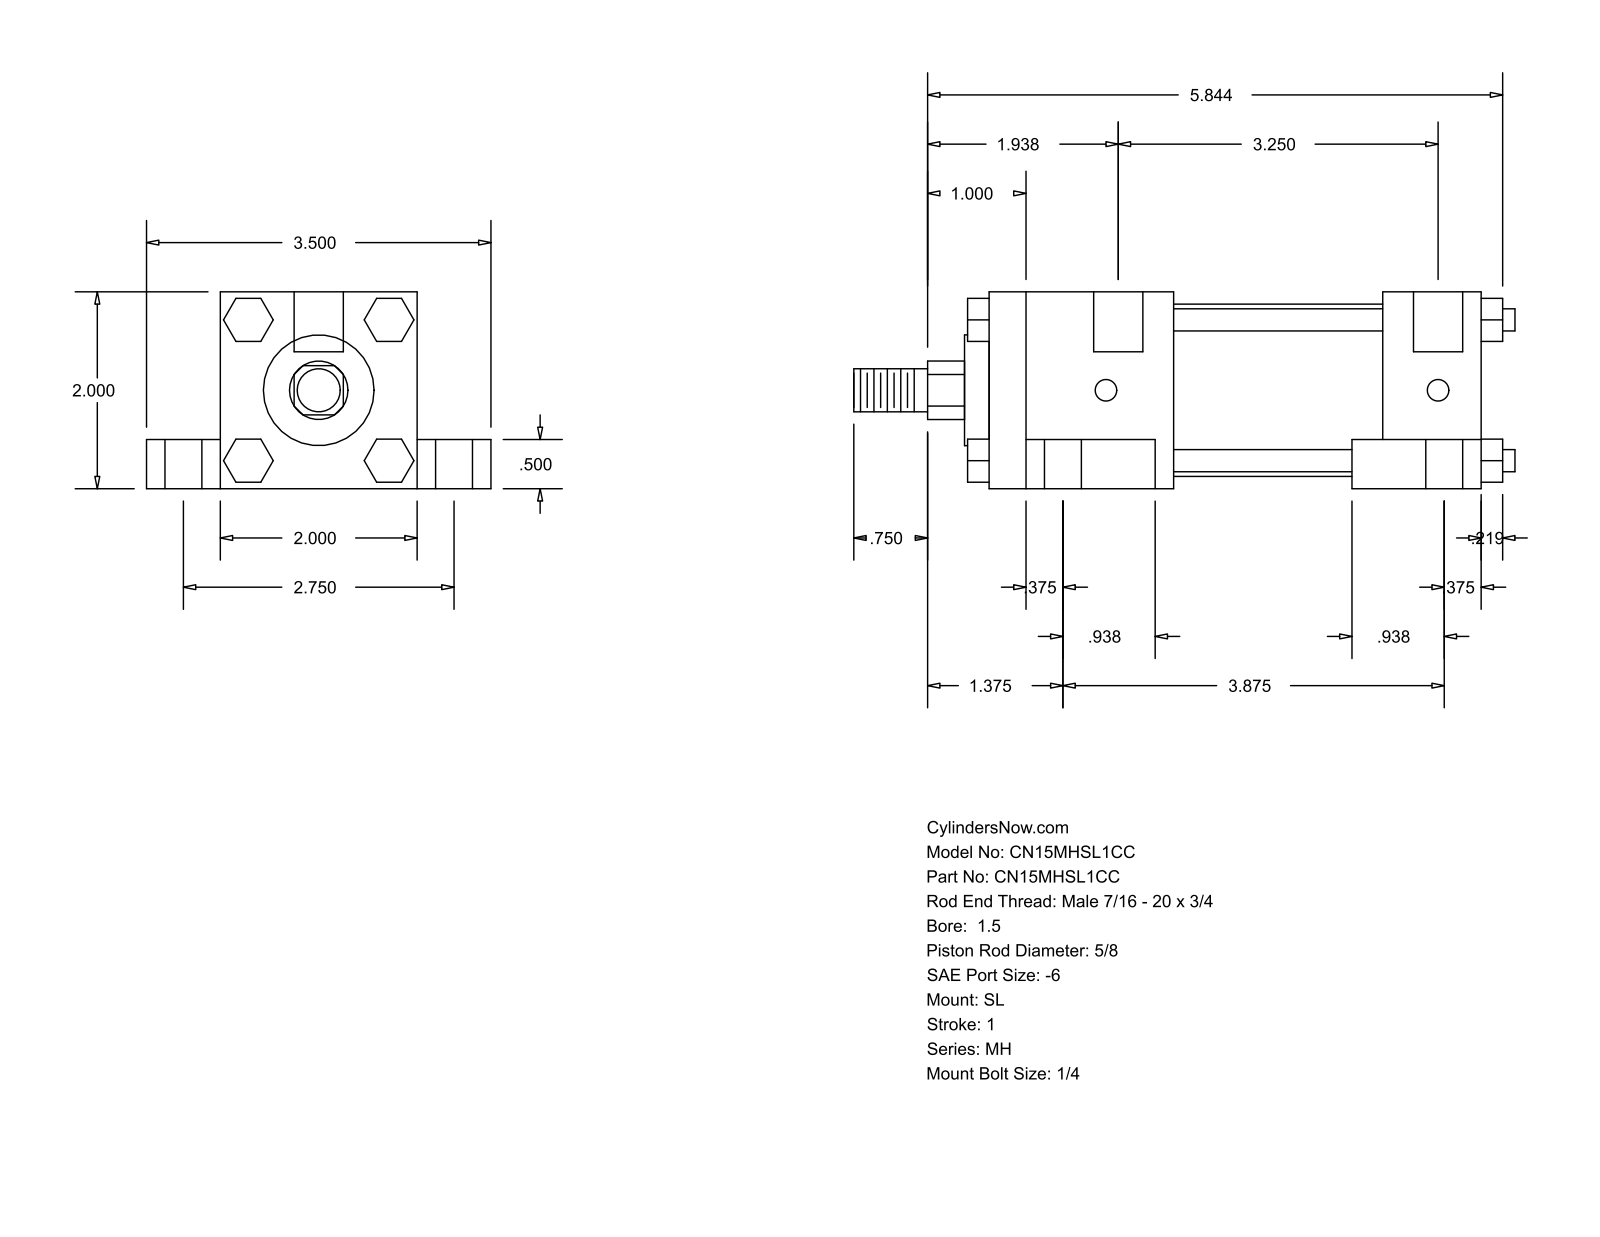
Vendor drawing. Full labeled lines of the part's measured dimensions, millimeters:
Part name (STEP PRODUCT): MH_SL__0150_0.625
STEP written by: GSSL Pune (CONFIG_CONTROL_DESIGN)
Units: millimetres
Bodies: 0 solids, 148 faces (112 planar, 36 cylindrical, 0 other)
Overall size (bounding box): 170.66 × 88.9 × 50.8
Round holes (diameter × count): ⌀5.56 ×4, ⌀9.53 ×4, ⌀15.88 ×4, ⌀12.7 ×2
Round bosses / shafts (diameter × count): ⌀5.71 ×4, ⌀44.45 ×1, ⌀28.57 ×1, ⌀15.88 ×1, ⌀11.11 ×1
Partial cylindrical surfaces — rounded edges, fillets, slot ends (radius × count): R7.54 ×1
Main face-to-face distances: 50.8, 38.1, 19.05, 12.7, 69.85, 127, 53.97, 9.52, 33.34, 84.14
Hole centre spacings: 34.96, 36.65, 37.73, 69.84, 85.72, 91.1, 94.03, 98.43
